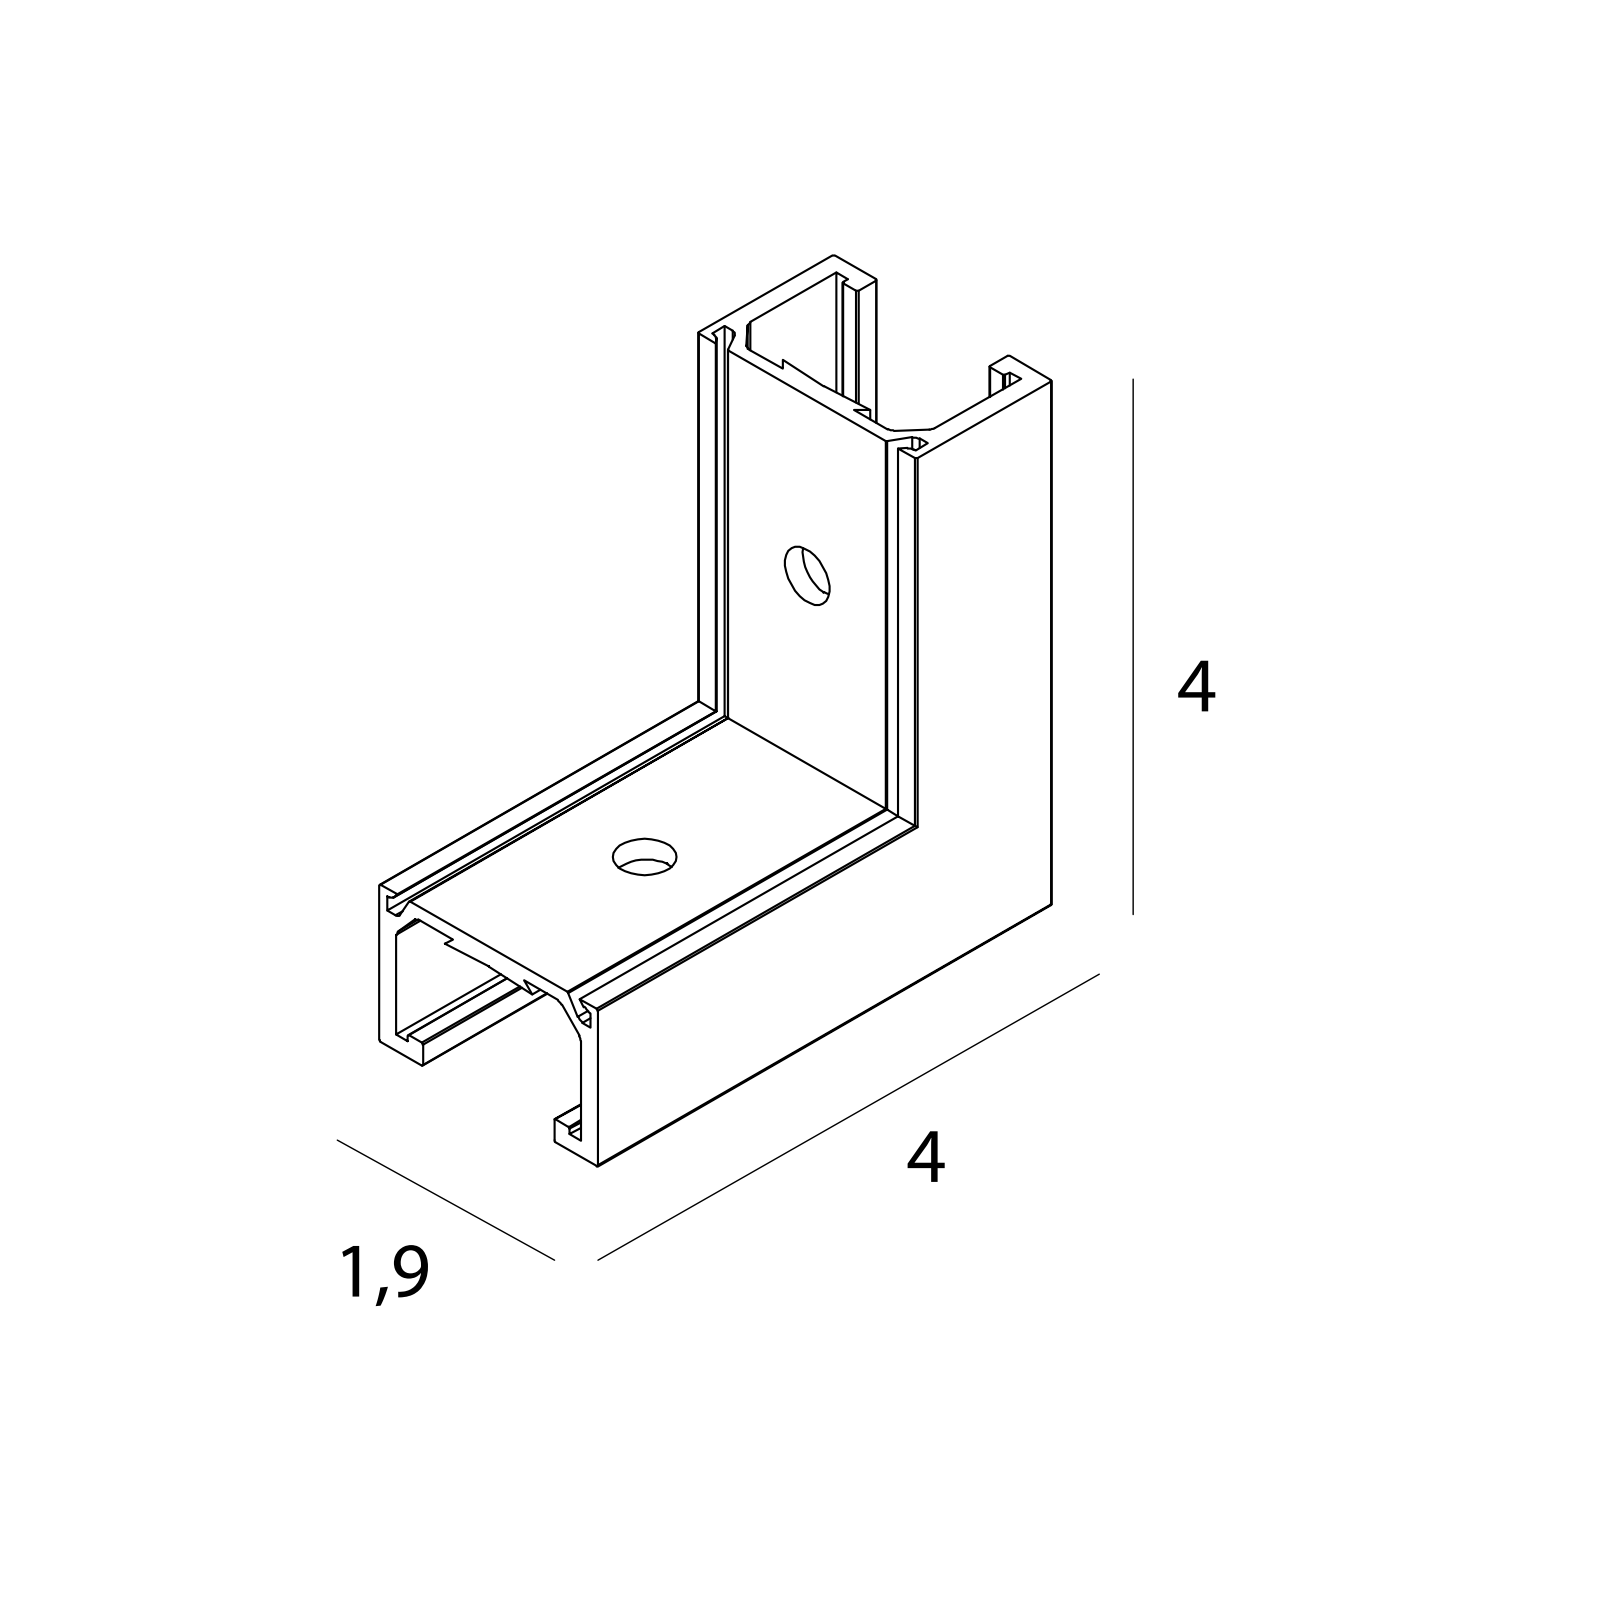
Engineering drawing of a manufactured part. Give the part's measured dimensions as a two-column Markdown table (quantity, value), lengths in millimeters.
| quantity | value |
| --- | --- |
| part name | NT0010 v3 |
| STEP written by | Autodesk Translation Framework v14.24.0.0 (AUTOMOTIVE_DESIGN) |
| units | millimeters |
| bodies | 1 solid, 116 faces (74 planar, 42 cylindrical, 0 other) |
| overall size | 40.09 × 40.09 × 19.3 |
| volume | 4 119 mm³ |
| surface area | 6 973 mm² |
| round holes (diameter × count) | 4 × 2 |
| partial cylindrical surfaces (radius × count) | 0.1 × 24, 0.5 × 16 |
| main face-to-face distances | 1.5, 17.8, 19.3, 12, 16.3, 1, 11, 3.85, 15.45, 2.35 |
